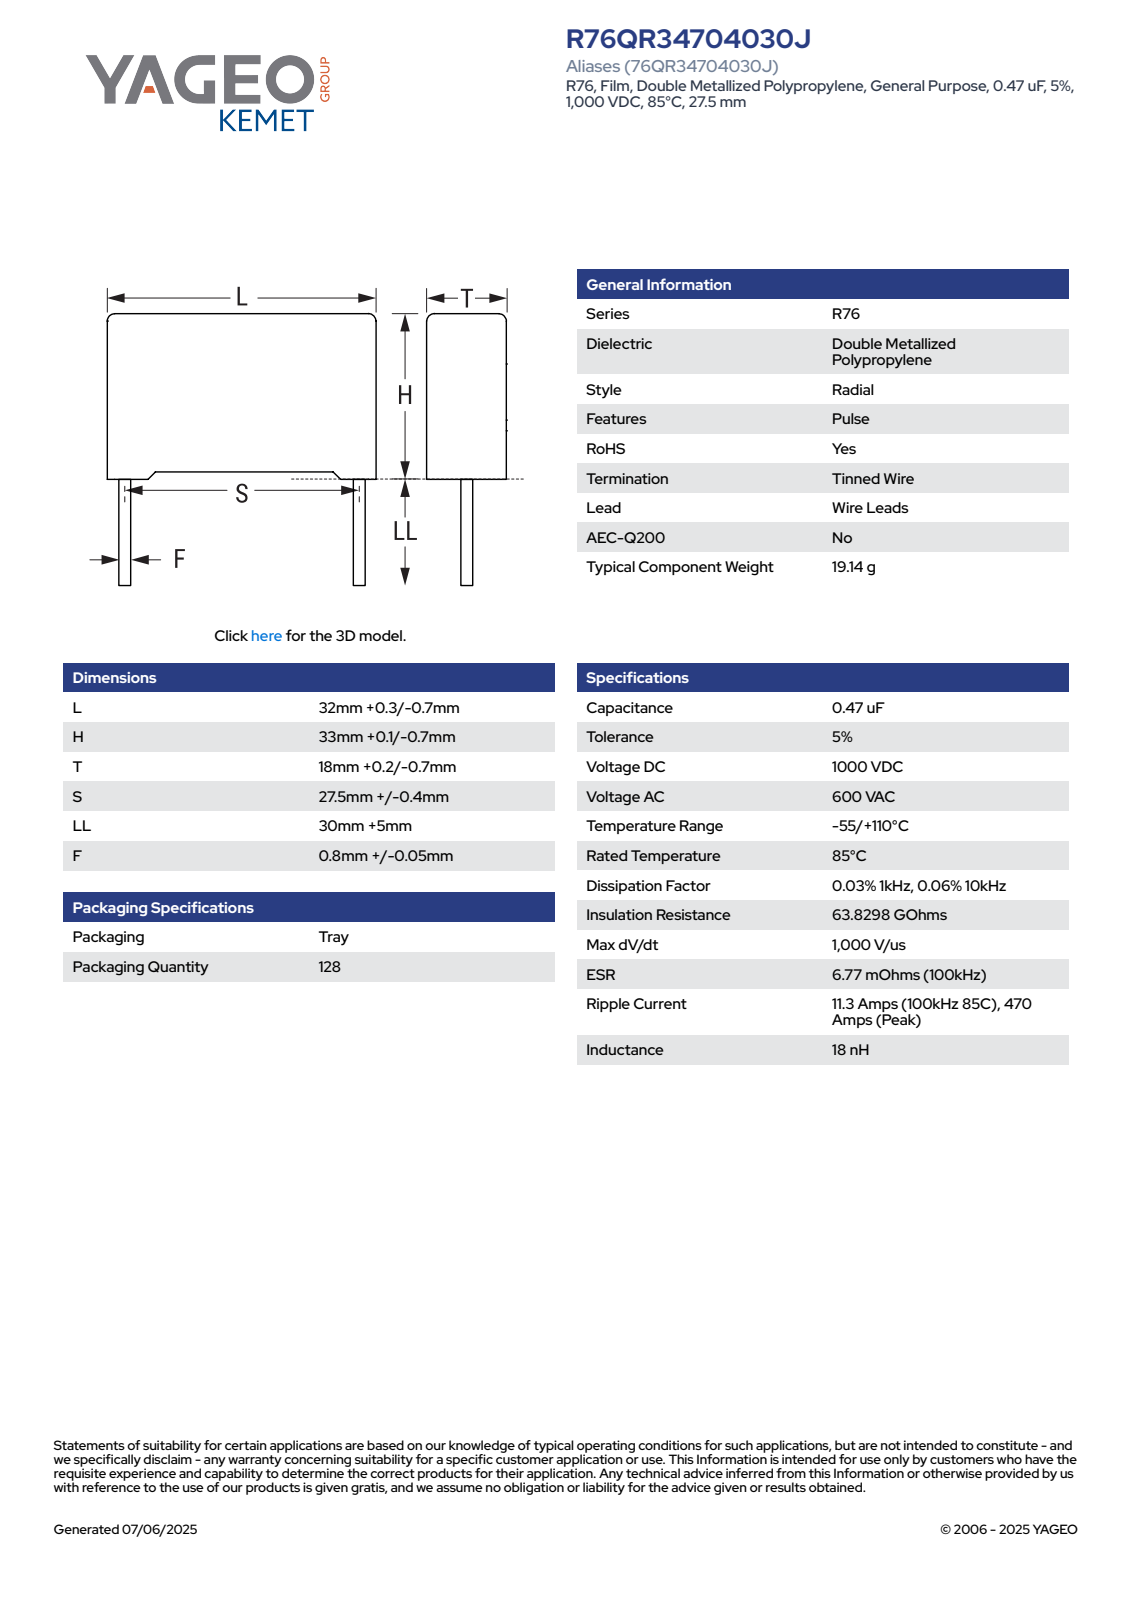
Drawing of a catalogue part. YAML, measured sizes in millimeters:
part_name: "CFR_RB2_32X33X18_L32.3H33.1T18.2S27.5LL35F0.85"
step_written_by: "SolidWorks 2021 (AUTOMOTIVE_DESIGN)"
units: millimeters
bodies: {solids: 4, faces: 85, planar: 77, cylindrical: 8, other: 0}
overall_size: [68.1, 32.3, 18.2]
volume: 18928
surface_area: 4754
round_bosses_or_shafts:
  - {diameter: 0.85, count: 2}
partial_cylinders:
  - {radius: 0.5, count: 4}
face_to_face_distances: [18.2, 32.3, 31.96, 0.39, 32.35, 0.75, 1.14, 33.1, 1.08, 31.22]
